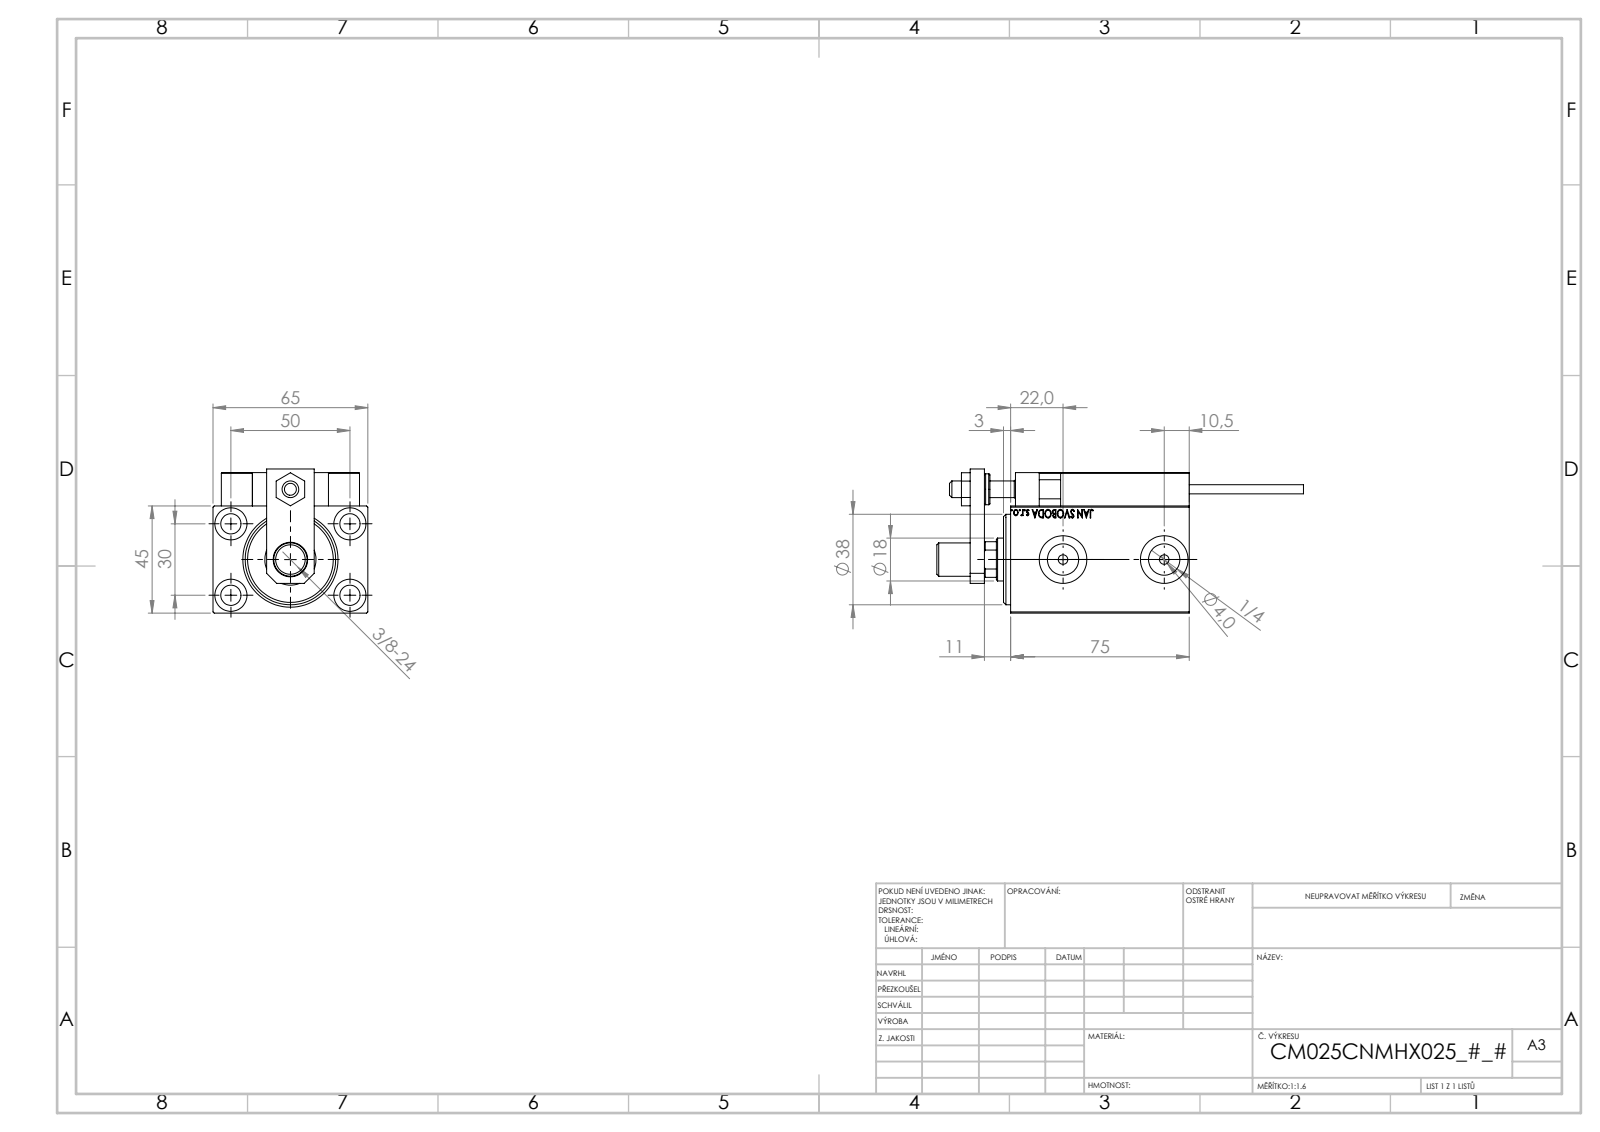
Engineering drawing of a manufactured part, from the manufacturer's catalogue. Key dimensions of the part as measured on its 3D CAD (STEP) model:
Part name (STEP PRODUCT): ALLEN BOLT D5; SWITCH_X_FRONT_BACK; Block; V450CM_VC_B (+7 more)
STEP written by: SolidWorks 2019 (CONFIG_CONTROL_DESIGN)
Units: millimetres
Bodies: 24 solids, 1295 faces (563 planar, 192 cylindrical, 540 other)
Overall size (bounding box): 154 × 65 × 60.5
Volume: 238 573 mm³ · Surface area: 72 805 mm²
Round holes (diameter × count): ⌀4 ×6, ⌀8 ×5, ⌀8.5 ×5, ⌀3.2 ×4, ⌀13.5 ×4, ⌀5 ×2, ⌀13.16 ×2, ⌀20 ×2, ⌀7 ×1, ⌀14.5 ×1, ⌀18 ×1, ⌀21.5 ×1
Round bosses / shafts (diameter × count): ⌀5 ×2, ⌀3.8 ×2, ⌀14 ×1, ⌀13 ×1, ⌀12 ×1, ⌀11 ×1
Partial cylindrical surfaces — rounded edges, fillets, slot ends (radius × count): R0.3 ×30, R3 ×2, R8.5 ×1
Main face-to-face distances: 45, 14, 65, 6, 59, 3, 19, 13, 20, 86
Hole centre spacings: 29.15, 11.37, 20, 27.07, 28.9, 29.59, 29.69, 30
